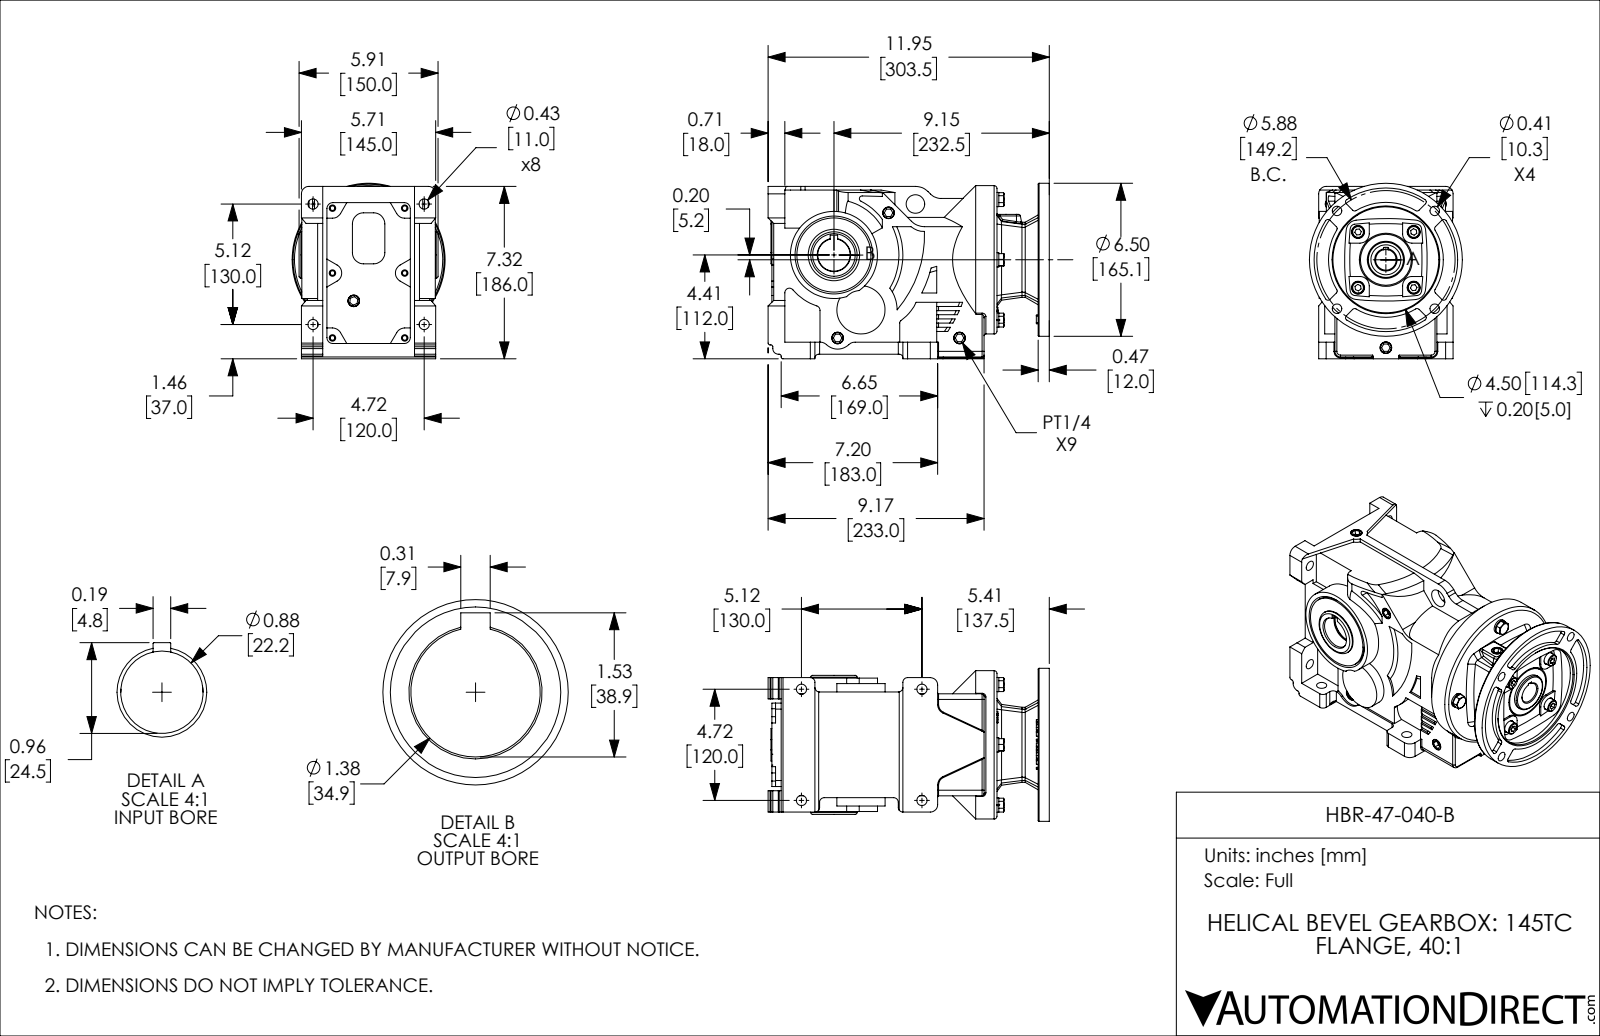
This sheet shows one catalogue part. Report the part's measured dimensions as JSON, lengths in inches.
{"part_name": "HBR-47-040-B", "step_written_by": "SolidWorks 2018 (AUTOMOTIVE_DESIGN)", "units": "inches", "bodies": {"solids": 1, "faces": 1020, "planar": 497, "cylindrical": 309, "other": 214}, "overall_size": [11.949, 7.455, 6.5], "volume_in3": 317.6, "surface_area_in2": 499.9, "round_holes": [[0.433, 8], [0.197, 6], [0.276, 6], [0.323, 4], [0.354, 4], [0.406, 4], [0.551, 4], [0.787, 1], [0.875, 1], [1.102, 1], [1.375, 1], [1.457, 1]], "round_bosses_or_shafts": [[0.606, 4], [0.512, 4], [0.315, 4], [6.5, 1], [6.299, 1], [3.701, 1], [3.15, 1], [2.165, 1]], "partial_cylinders_radius": [[0.118, 18], [0.079, 14], [0.394, 14], [0.197, 10], [0.472, 9], [0.157, 6], [0.039, 5], [0.256, 4]], "face_to_face_distances": [0.197, 0.079, 4.331, 1.752, 11.319, 0.157, 0.118, 0.512, 0.394, 0.315], "hole_center_spacings": [1.815, 2.132, 3.381, 3.925, 5.08, 1.673, 5.118, 1.265]}
